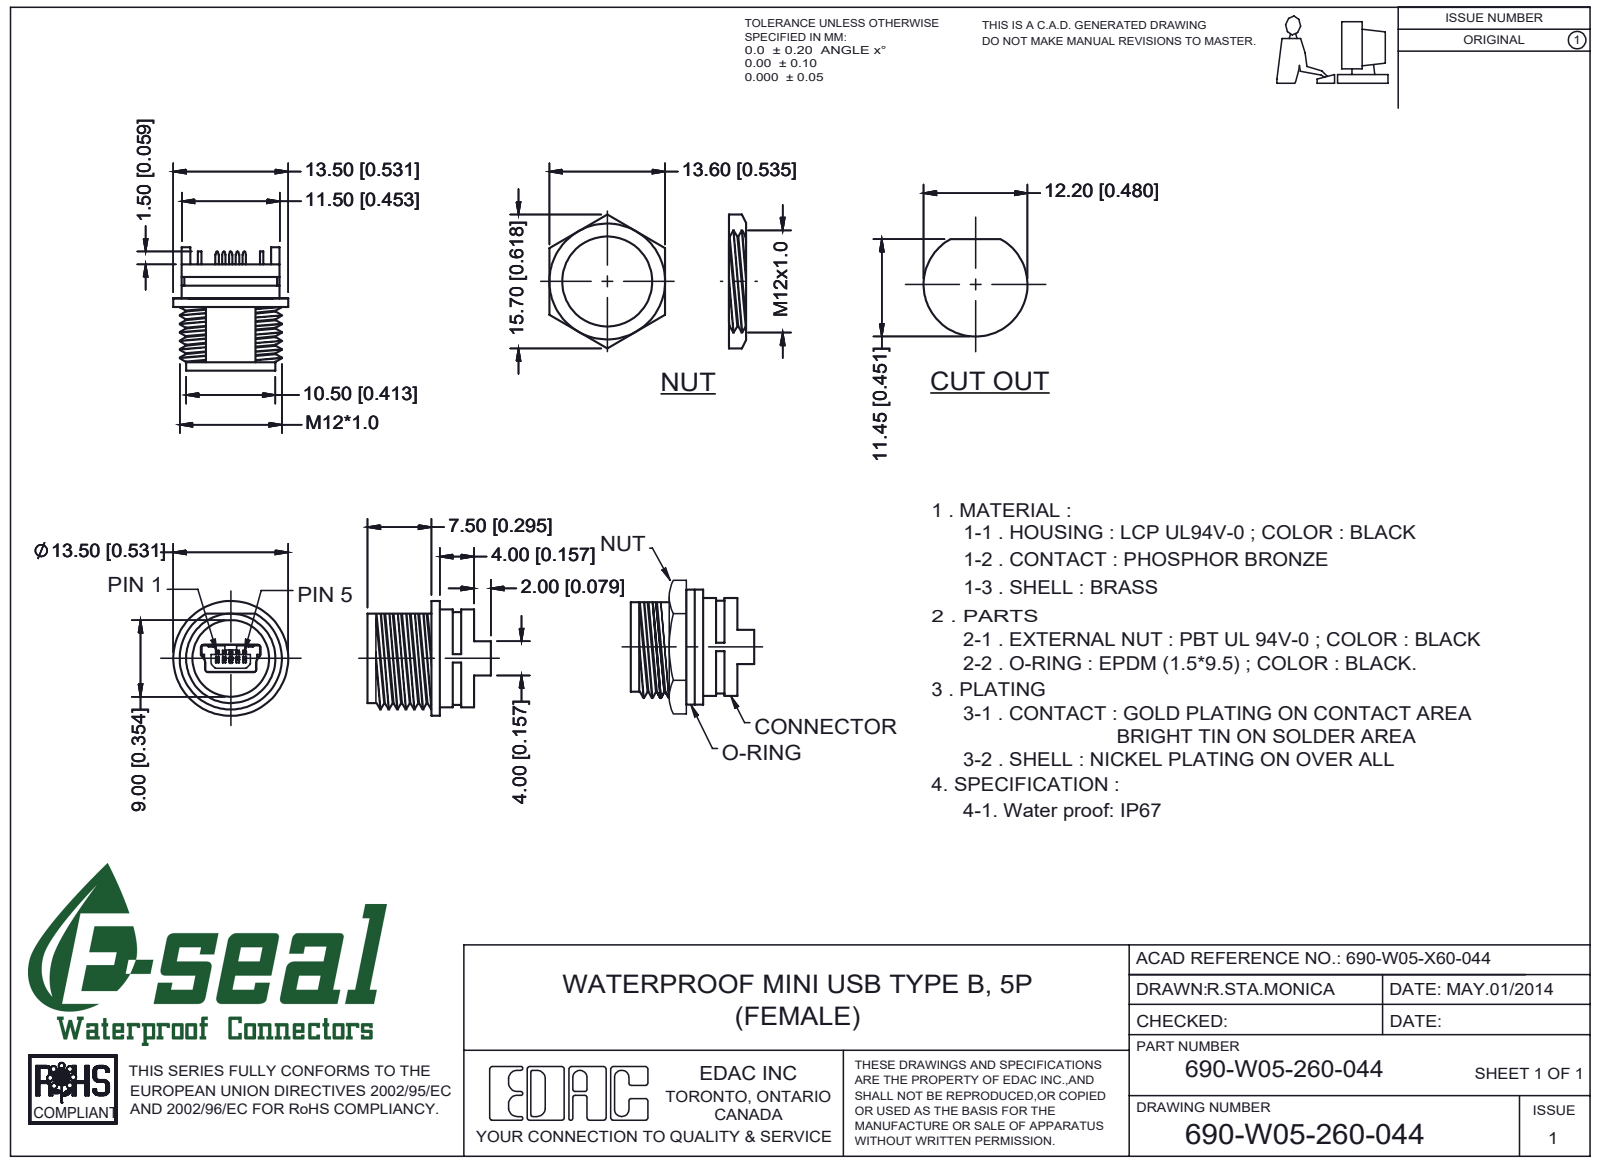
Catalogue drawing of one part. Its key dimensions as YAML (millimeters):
part_name: "690-W05-260-044"
step_written_by: "SolidWorks 2020 (AUTOMOTIVE_DESIGN)"
units: millimeters
bodies: {solids: 1, faces: 885, planar: 593, cylindrical: 235, other: 57}
overall_size: [15.7, 14.5, 14.2]
volume: 913
surface_area: 2247
round_holes:
  - {diameter: 9, count: 1}
  - {diameter: 9.5, count: 1}
round_bosses_or_shafts:
  - {diameter: 13.5, count: 1}
  - {diameter: 12, count: 1}
  - {diameter: 11.5, count: 1}
  - {diameter: 10.9, count: 1}
  - {diameter: 10.5, count: 1}
partial_cylinders:
  - {radius: 0.2, count: 53}
  - {radius: 0.15, count: 23}
  - {radius: 0.4, count: 12}
  - {radius: 0.6, count: 11}
  - {radius: 0.55, count: 8}
  - {radius: 0.3, count: 6}
  - {radius: 0.12, count: 5}
  - {radius: 0.19, count: 4}
face_to_face_distances: [2.95, 0.4, 3.2, 3.95, 5.45, 3.5, 1.5, 2.25, 0.75, 4]
